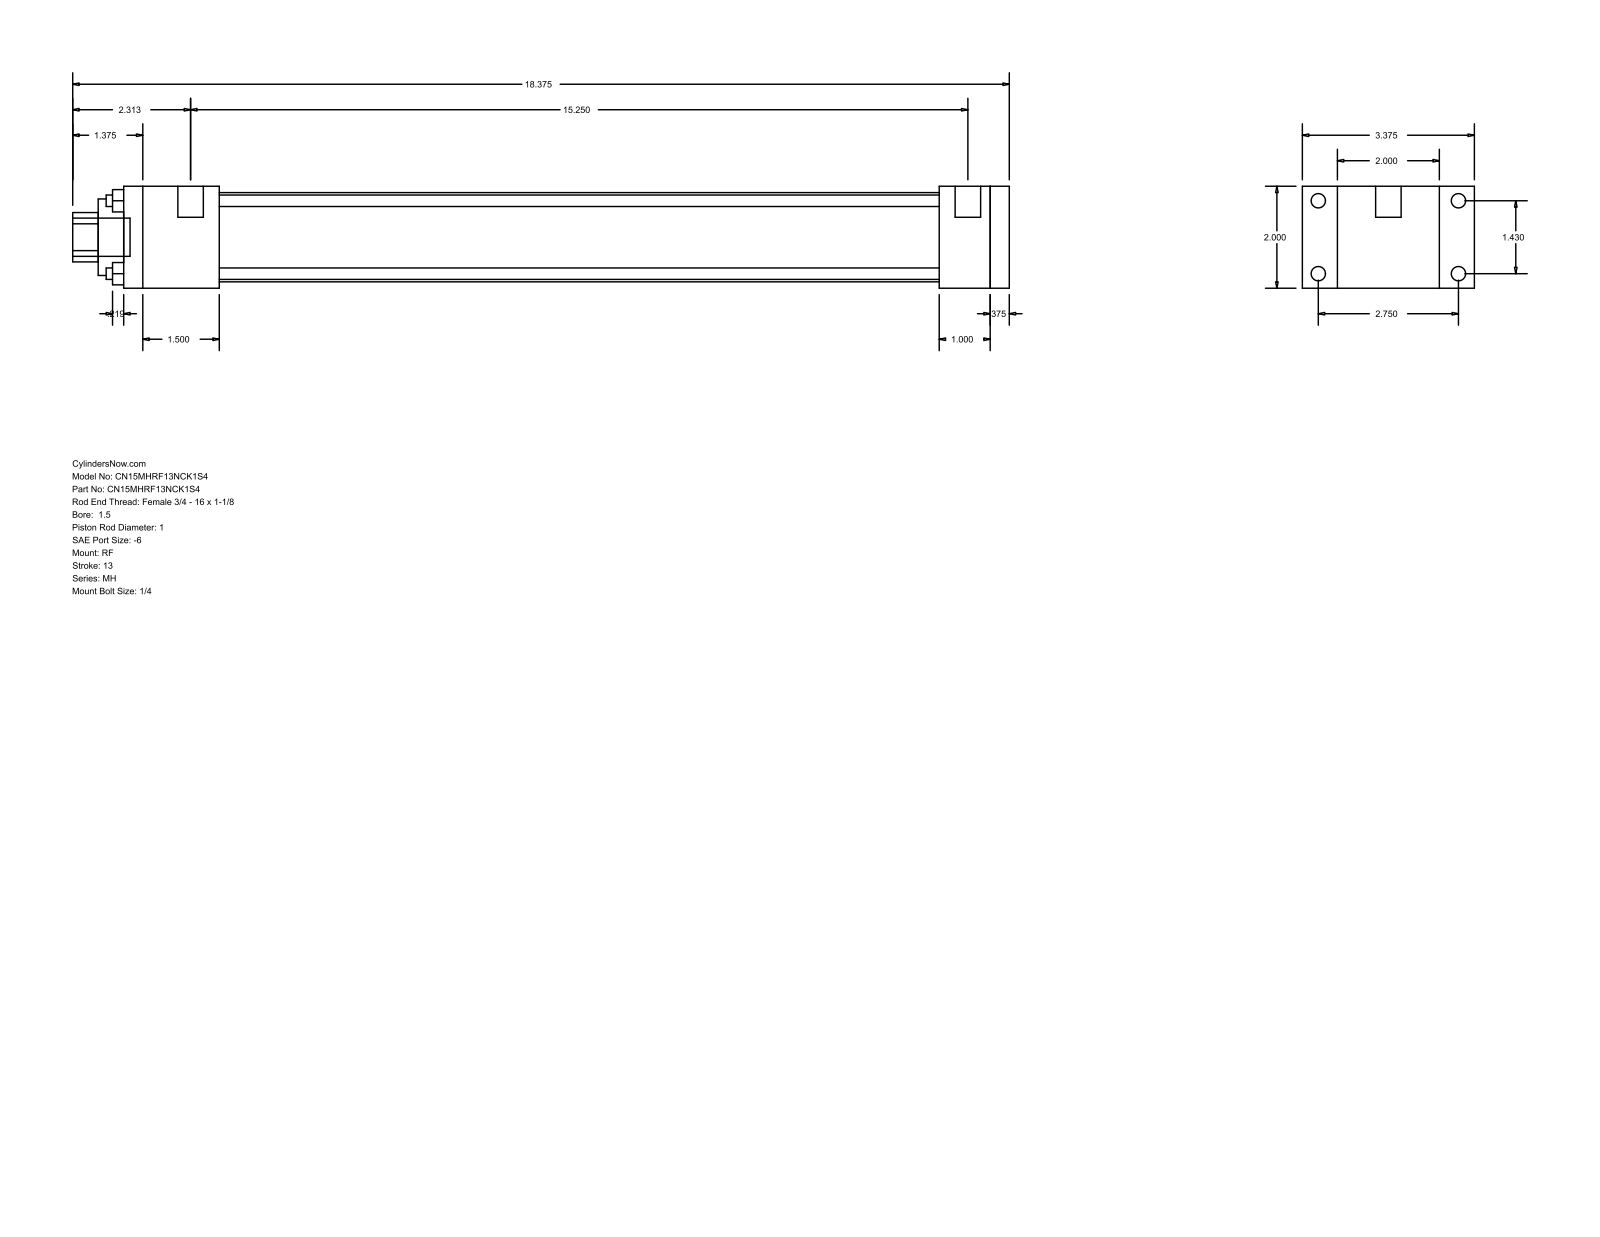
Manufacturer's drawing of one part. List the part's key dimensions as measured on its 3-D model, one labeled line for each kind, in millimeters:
Part name (STEP PRODUCT): MH_RF__0150_1
STEP written by: GSSL Pune (CONFIG_CONTROL_DESIGN)
Units: millimetres
Bodies: 0 solids, 92 faces (64 planar, 28 cylindrical, 0 other)
Overall size (bounding box): 466.73 × 85.72 × 50.8
Round holes (diameter × count): ⌀5.71 ×4, ⌀25.4 ×1, ⌀38.1 ×1, ⌀44.45 ×1
Round bosses / shafts (diameter × count): ⌀7.14 ×4, ⌀5.56 ×4, ⌀12.7 ×2, ⌀19.05 ×1
Partial cylindrical surfaces — rounded edges, fillets, slot ends (radius × count): R12.29 ×1
Main face-to-face distances: 50.8, 9.53, 431.8, 25.4, 441.33, 17.46, 68.26, 406.4, 34.93, 47.63
Hole centre spacings: 25.68, 36.32, 51.36
